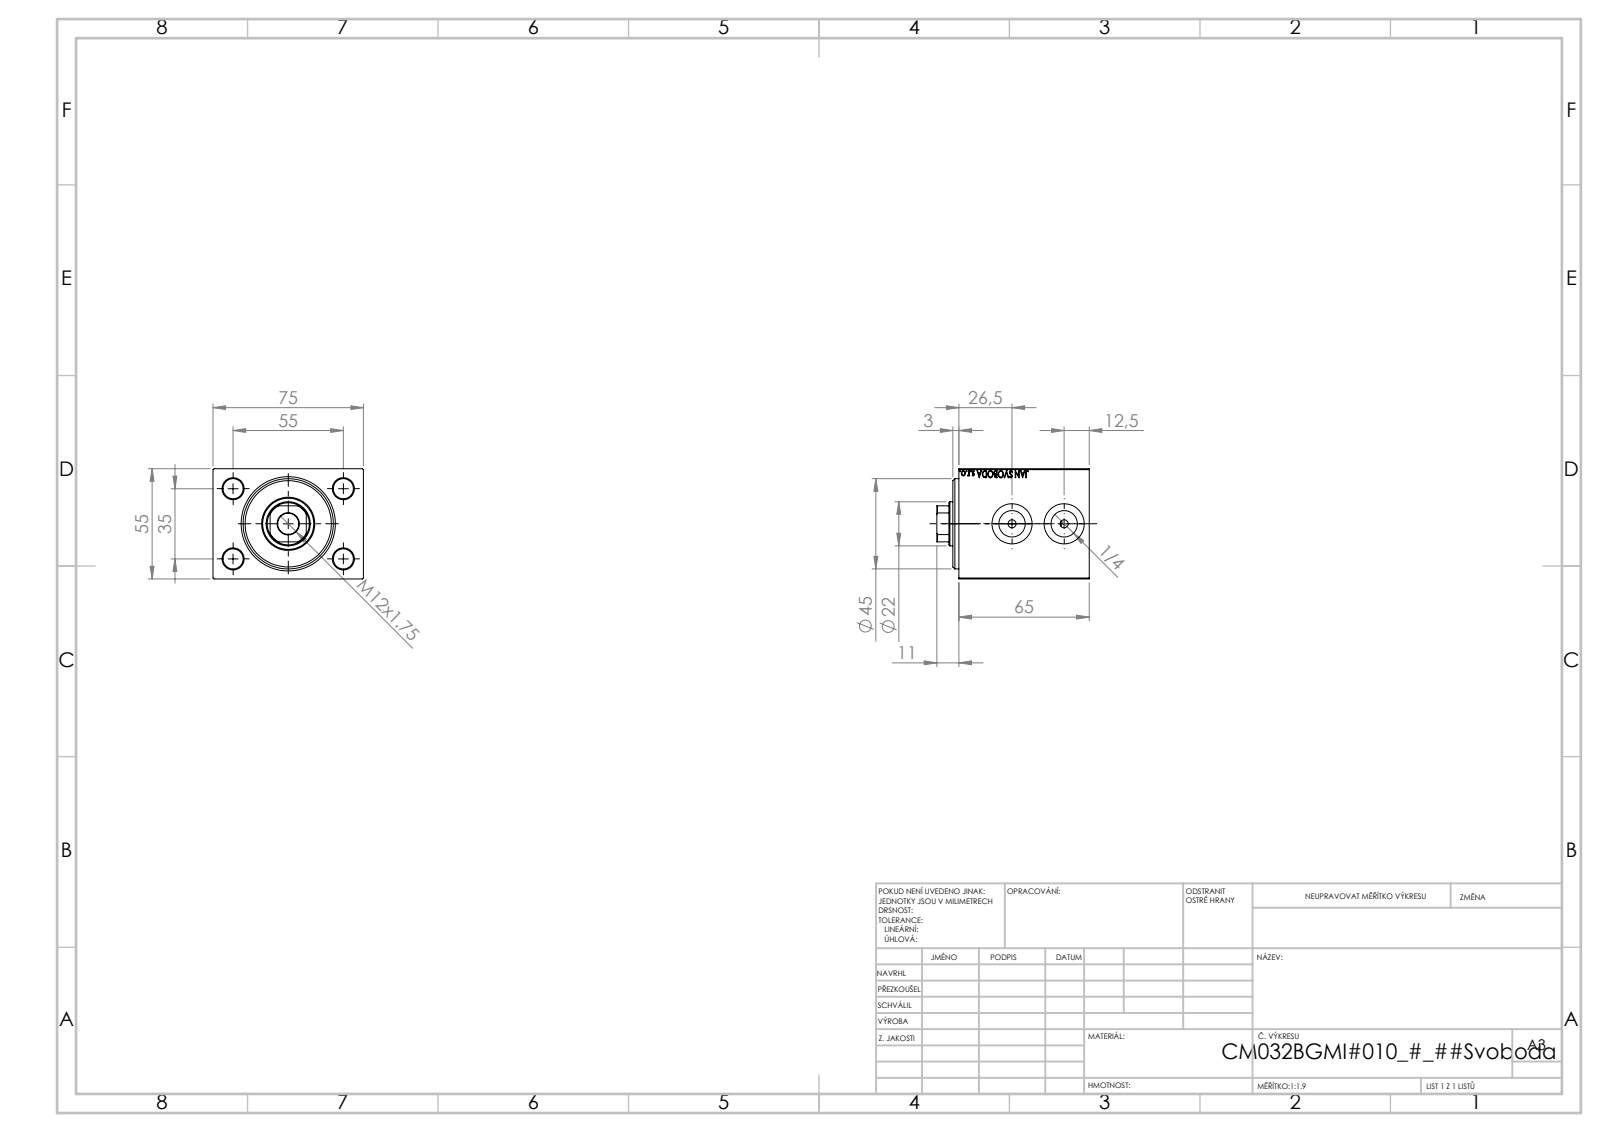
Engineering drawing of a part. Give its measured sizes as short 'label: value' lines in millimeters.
name: V450CM_B_VCP; V450CM_B_Body; V450CM_VC_B
written by: SolidWorks 2019 (CONFIG_CONTROL_DESIGN)
unit: mm
bodies: 3 solids, 882 faces (402 planar, 54 cylindrical, 426 other)
size: 76 × 75 × 55
volume: 251 979 mm³; area: 51 007 mm²
holes: 4× ⌀10, 2× ⌀4, 2× ⌀13.16, 2× ⌀20, 1× ⌀10.5, 1× ⌀22, 1× ⌀25.5, 1× ⌀26.5, 1× ⌀32, 1× ⌀34, 1× ⌀45
rounds: 1× R10.5
face distances: 55, 75, 65, 14, 51, 5, 46, 60, 8, 54
hole spacings: 32.6, 35, 55, 65.19, 26
